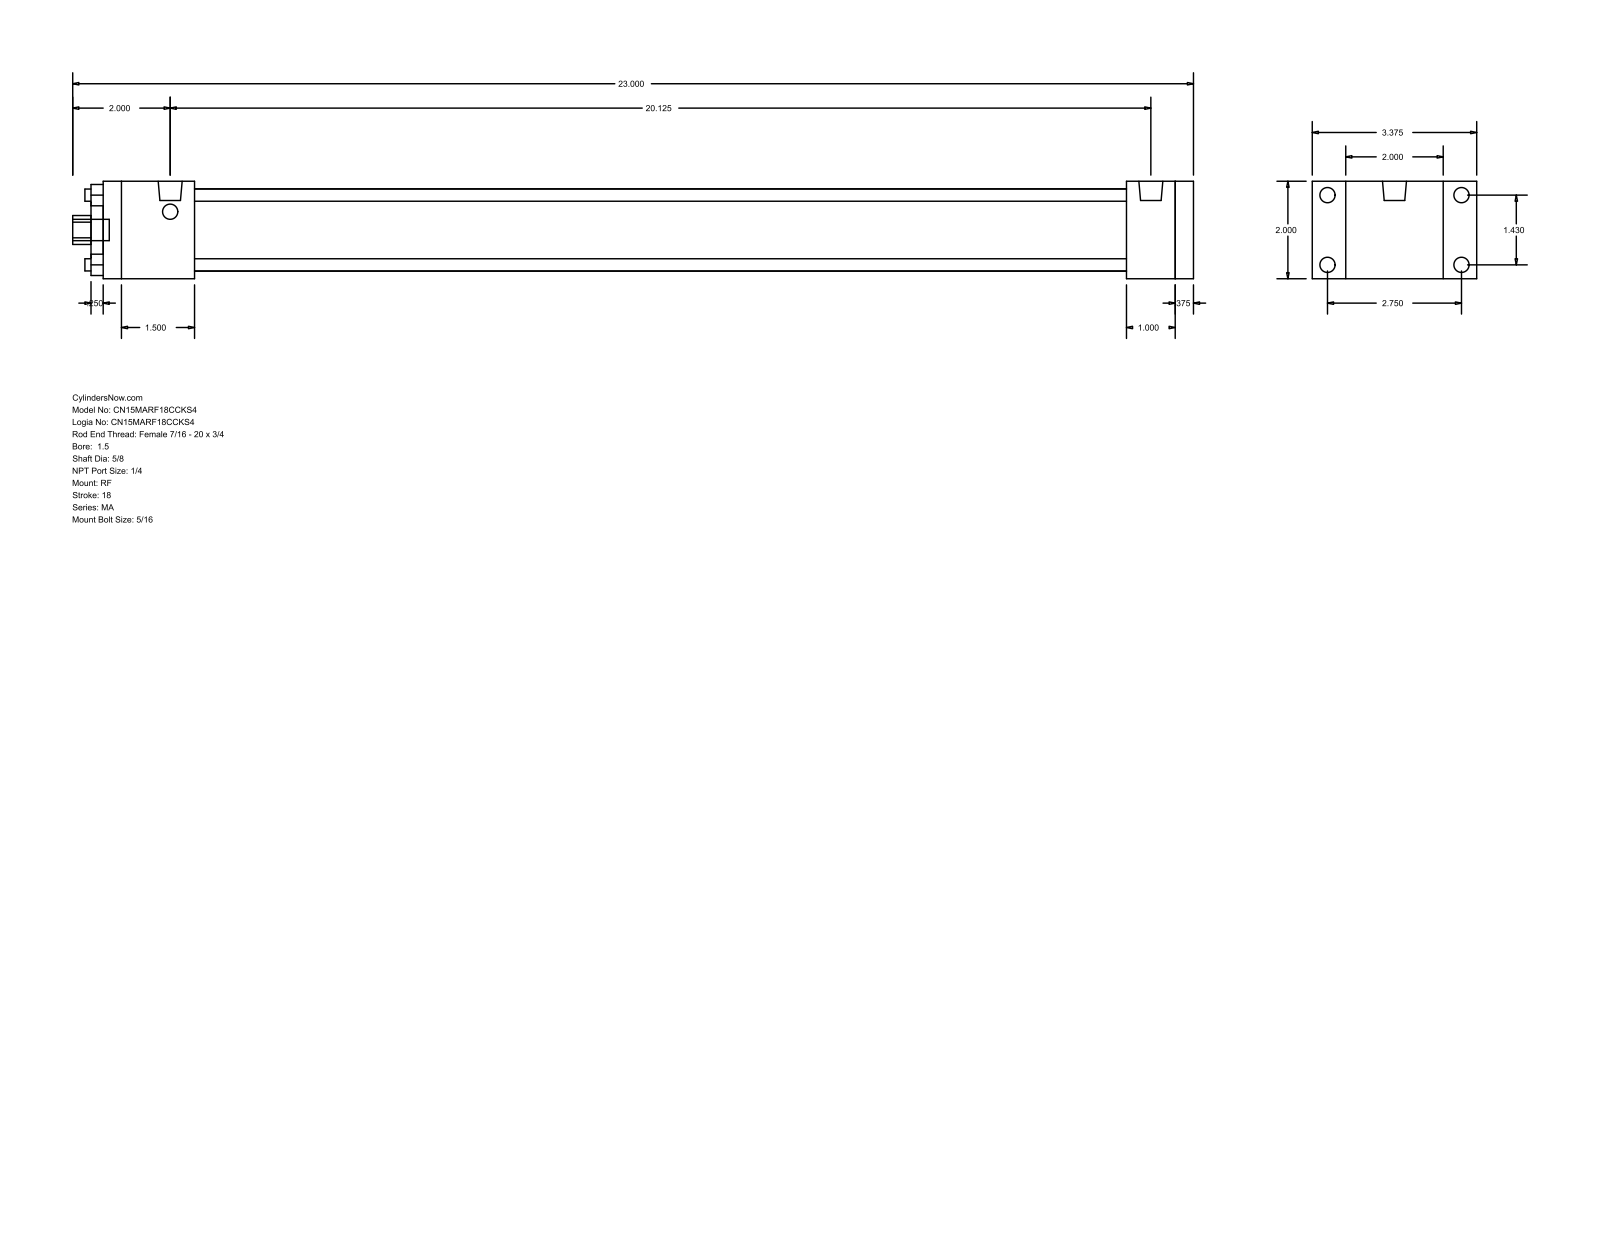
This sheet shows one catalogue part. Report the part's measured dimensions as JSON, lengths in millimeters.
{"part_name": "MA_RF__0150_0.625", "step_written_by": "GSSL Pune (CONFIG_CONTROL_DESIGN)", "units": "millimeters", "bodies": {"solids": 0, "faces": 92, "planar": 64, "cylindrical": 28, "other": 0}, "overall_size": [584.2, 85.72, 50.8], "round_holes": [[6.35, 4], [15.88, 1], [28.57, 1], [42.93, 1]], "round_bosses_or_shafts": [[7.94, 8], [12.49, 2], [11.11, 1]], "partial_cylinders_radius": [[7.54, 1]], "face_to_face_distances": [50.8, 9.53, 568.32, 558.79, 533.39, 25.4, 34.93, 47.62, 485.77, 511.17], "hole_center_spacings": [25.68, 36.32, 51.36]}
